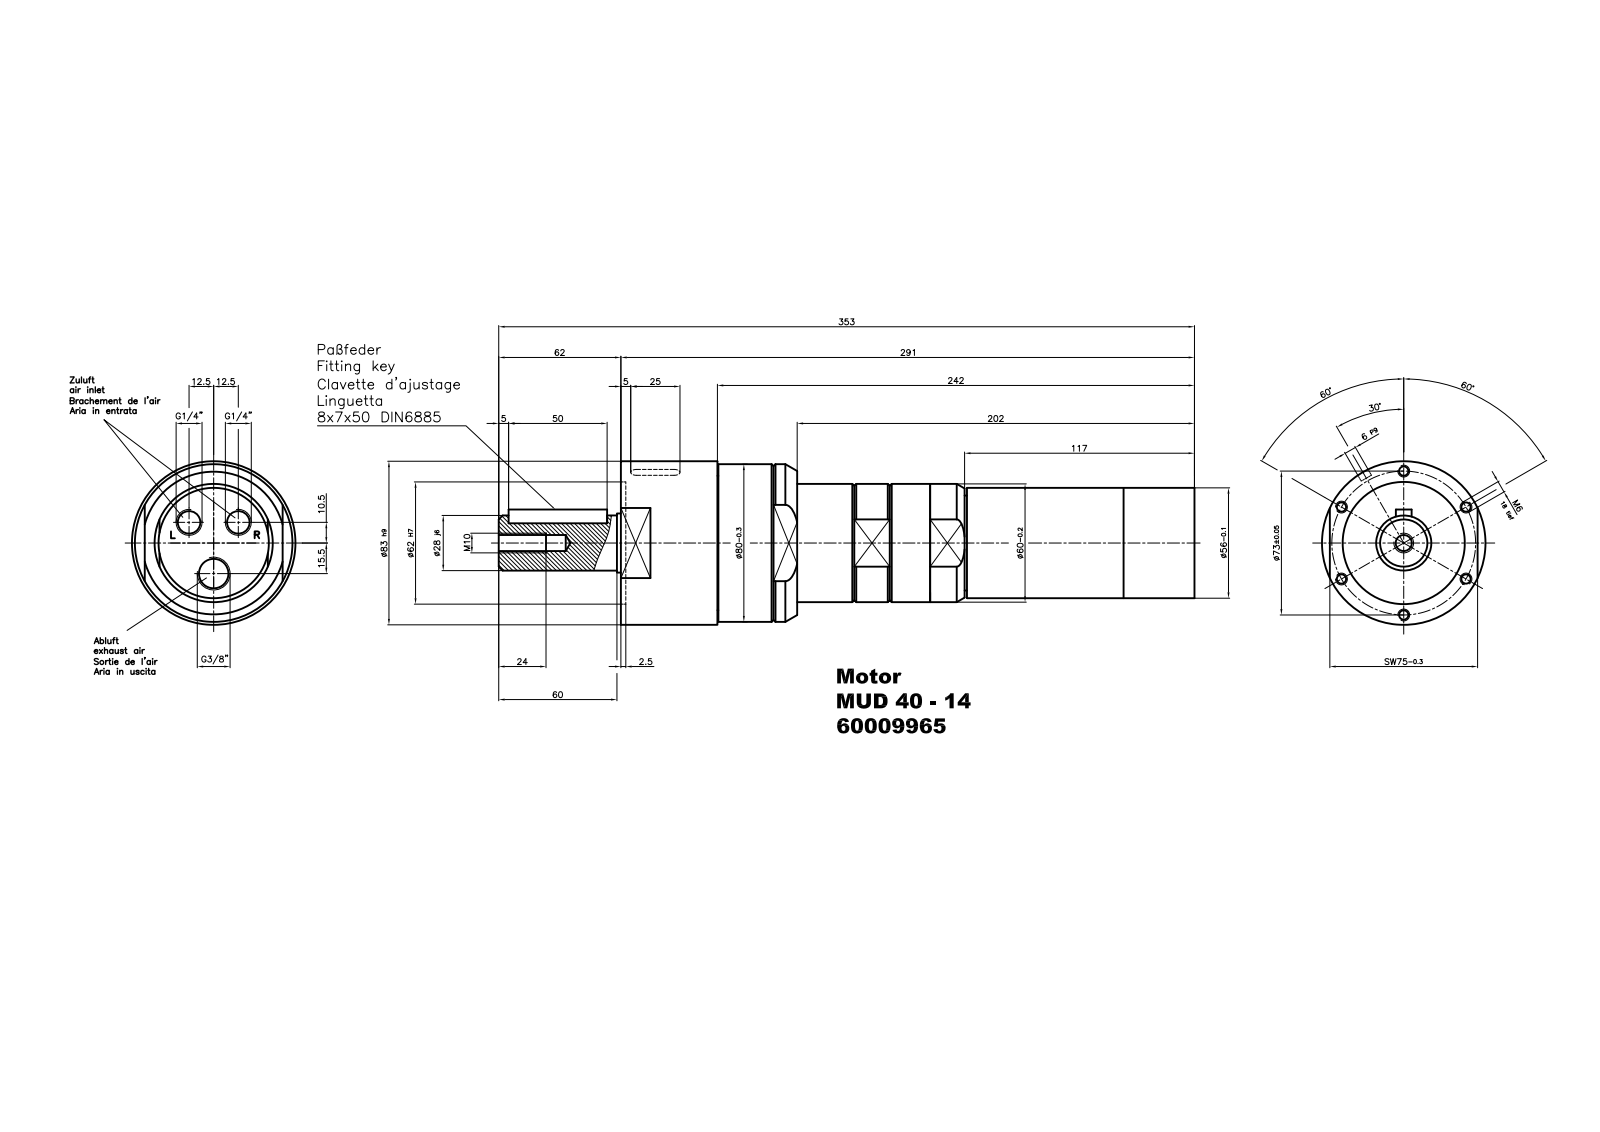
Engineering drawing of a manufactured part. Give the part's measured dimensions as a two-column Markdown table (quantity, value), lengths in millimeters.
| quantity | value |
| --- | --- |
| part name | MUD 40-14_60009965 |
| STEP written by | Autodesk Inventor 2008 (CONFIG_CONTROL_DESIGN) |
| units | millimeters |
| bodies | 1 solid, 373 faces (135 planar, 197 cylindrical, 41 other) |
| overall size | 353.2 × 83 × 83 |
| volume | 999 024 mm³ |
| surface area | 97 994 mm² |
| round holes (diameter × count) | 4.92 × 3, 4.92 × 3, 1.55 × 2, 2.5 × 2, 4 × 2, 5.5 × 2, 11.44 × 2, 8.38 × 1, 14.95 × 1, 38 × 1, 58.69 × 1, 62 × 1 |
| round bosses / shafts (diameter × count) | 5 × 2, 3.6 × 2, 83 × 1, 80 × 1, 68.18 × 1, 60 × 1, 56 × 1, 48.18 × 1 |
| partial cylindrical surfaces (radius × count) | 5.25 × 68, 2.25 × 2, 3 × 2, 4 × 2, 26.47 × 1, 28.36 × 1, 32.5 × 1, 34.69 × 1 |
| main face-to-face distances | 291.2, 49, 242.2, 0.5, 44.5, 5, 89.5, 40.5, 201.7, 44 |
| hole center spacings | 36.5, 63.22, 16.32, 28.85, 36.49, 73, 9.52, 14.04 |
